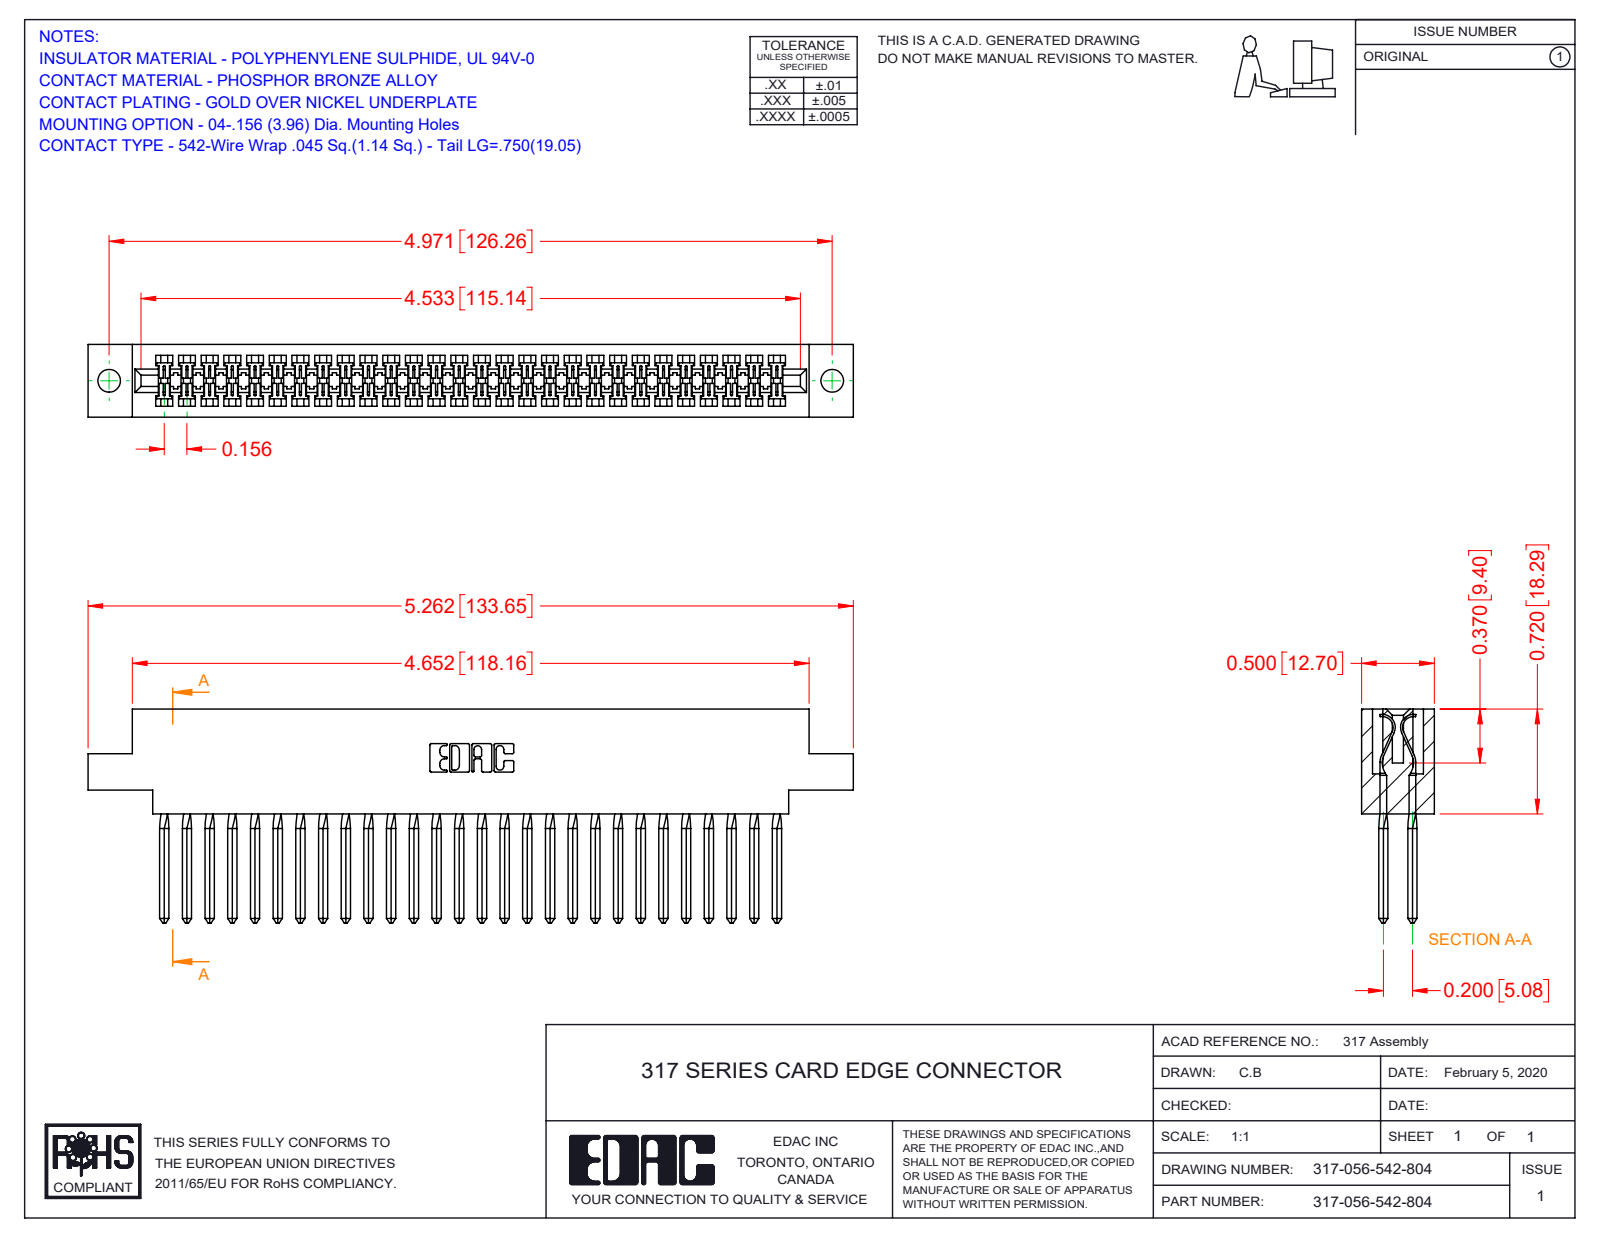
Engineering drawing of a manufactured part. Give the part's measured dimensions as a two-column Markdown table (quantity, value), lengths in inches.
| quantity | value |
| --- | --- |
| part name | 317 Part_.156 Dia - TH; 317-290-003_542; 317-056-542-804 |
| STEP written by | SolidWorks 2016 (CONFIG_CONTROL_DESIGN) |
| units | inches |
| bodies | 57 solids, 3294 faces (2634 planar, 436 cylindrical, 224 other) |
| overall size | 5.262 × 1.47 × 0.5 |
| volume | 1.303 in³ |
| surface area | 45.05 in² |
| round holes (diameter × count) | 0.156 × 2 |
| partial cylindrical surfaces (radius × count) | 0.006 × 112, 0.01 × 22, 0.007 × 6, 0.031 × 6, 0.026 × 3, 0.074 × 2, 0.089 × 2, 0.1 × 2 |
| main face-to-face distances | 0.5, 0.075, 0.425, 0.35, 0.2, 0.11, 0.116, 0.046, 0.128, 0.372 |
| hole center spacings | 4.971 |
